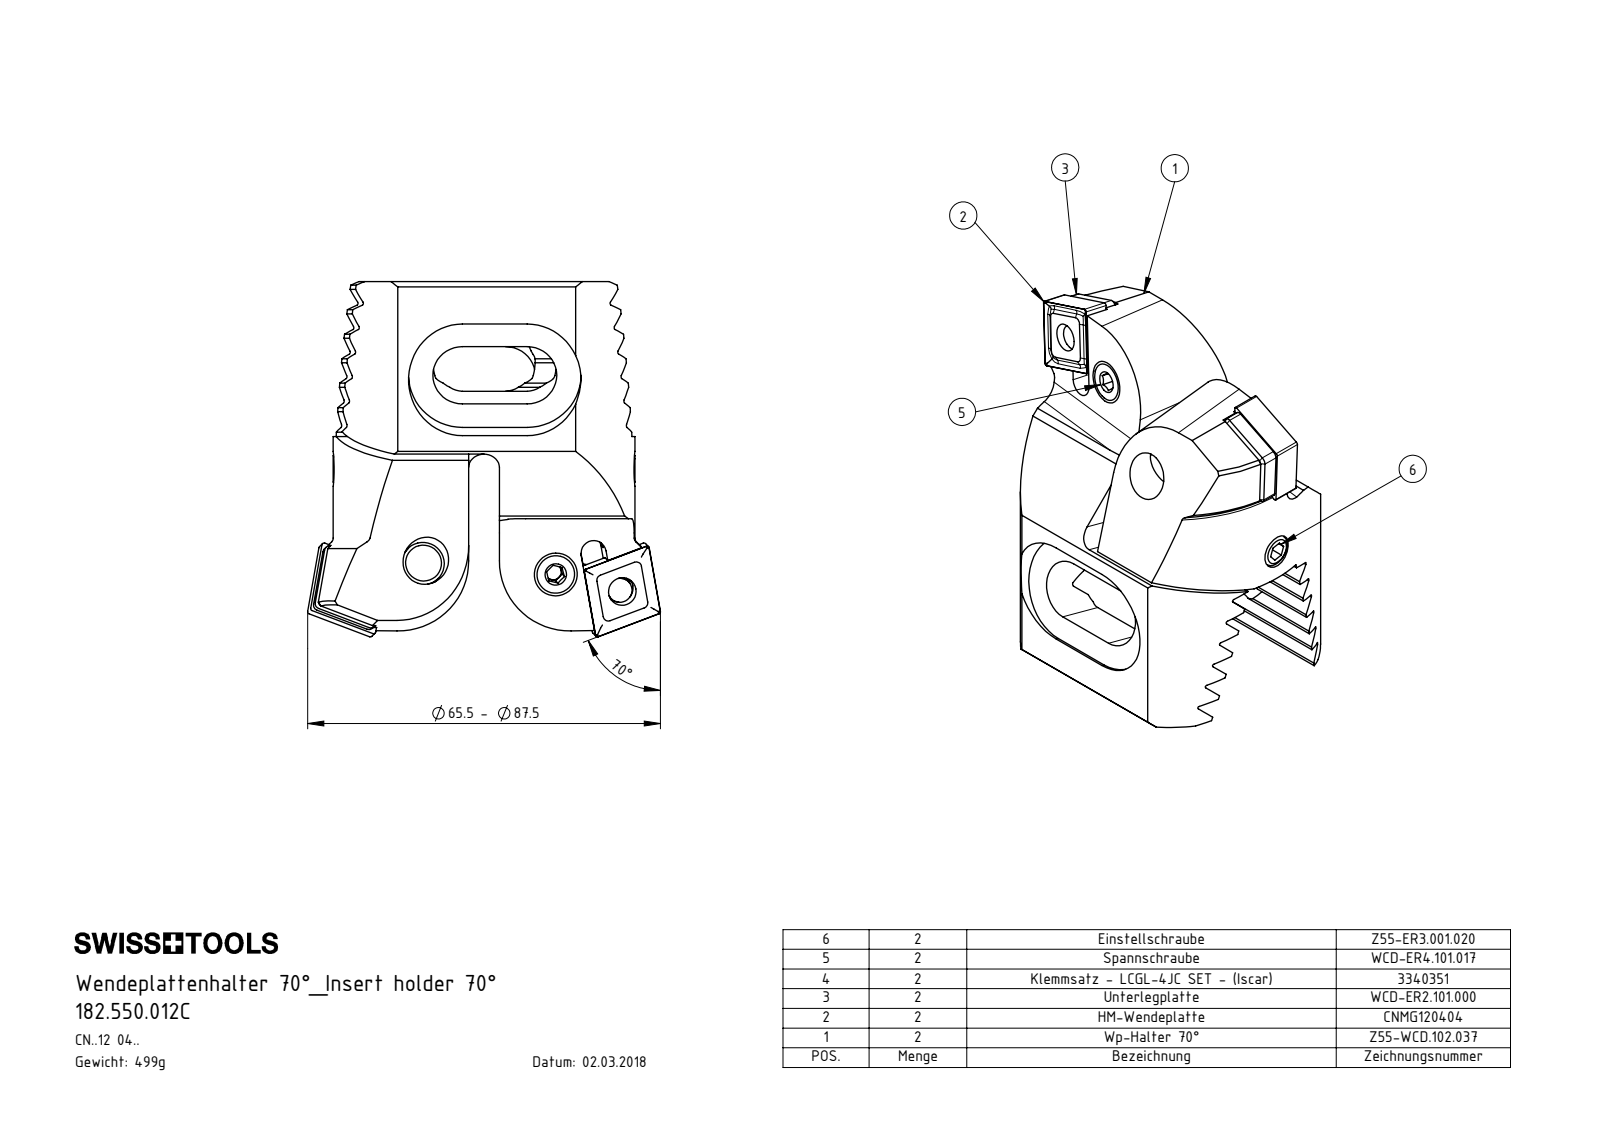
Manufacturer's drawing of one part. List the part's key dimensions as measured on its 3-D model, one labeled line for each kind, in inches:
Part name (STEP PRODUCT): WCD-ER4.101.017_A; WCD; WCD-ER3.101.000_A; 182.550.012C (+5 more)
STEP written by: SolidWorks 2017 (CONFIG_CONTROL_DESIGN)
Units: inches
Bodies: 14 solids, 578 faces (244 planar, 164 cylindrical, 170 other)
Overall size (bounding box): 2.595 × 2.579 × 1.732
Volume: 3.83 in³ · Surface area: 40.85 in²
Round holes (diameter × count): ⌀0.039 ×2, ⌀0.203 ×2, ⌀0.252 ×2, ⌀0.276 ×2, ⌀0.331 ×2, ⌀0.197 ×1
Round bosses / shafts (diameter × count): ⌀0.315 ×2, ⌀0.311 ×2, ⌀0.252 ×2, ⌀0.177 ×2, ⌀0.14 ×2, ⌀0.236 ×1, ⌀0.157 ×1
Partial cylindrical surfaces — rounded edges, fillets, slot ends (radius × count): R0.013 ×12, R0.039 ×10, R0.016 ×8, R0.098 ×6, R0.118 ×4, R0.217 ×4, R0.394 ×4, R0.083 ×2
Main face-to-face distances: 0.16, 0.32, 0.481, 0.641, 0.801, 0.039, 0.28, 1.732, 0.176, 1.132
Hole centre spacings: 0.504, 0.591, 0.506, 0.506, 1.141
